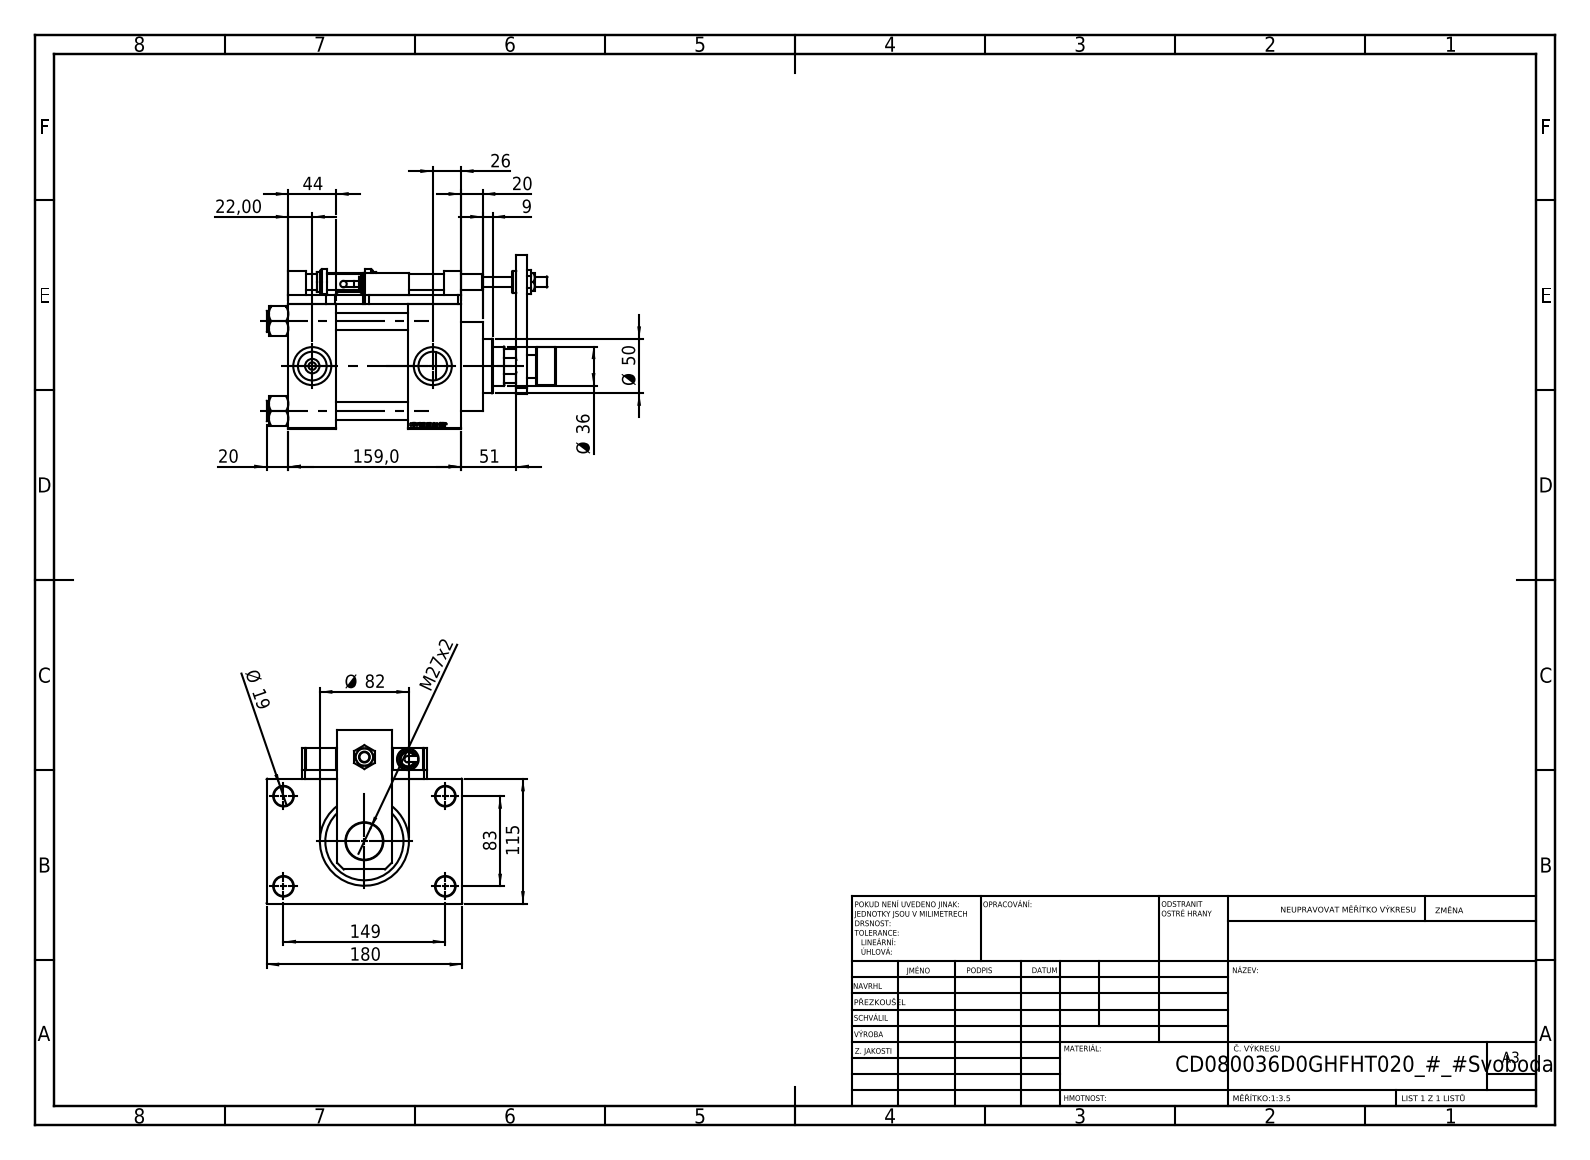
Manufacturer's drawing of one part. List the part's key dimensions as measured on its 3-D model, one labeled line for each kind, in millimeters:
Part name (STEP PRODUCT): V215CD_NUT_M5_D; V215CD_SWITCH_Q_BLOK; V215CD_SWITCH_Q_NUT10; V215CR_ROD_END_F (+7 more)
STEP written by: SolidWorks 2019 (CONFIG_CONTROL_DESIGN)
Units: millimetres
Bodies: 25 solids, 1393 faces (670 planar, 160 cylindrical, 563 other)
Overall size (bounding box): 266 × 180 × 160
Volume: 2 297 000 mm³ · Surface area: 393 388 mm²
Round holes (diameter × count): ⌀8.5 ×4, ⌀13.5 ×4, ⌀16 ×4, ⌀18 ×4, ⌀7 ×2, ⌀26.44 ×2, ⌀35 ×2, ⌀10 ×1, ⌀14 ×1, ⌀25.5 ×1, ⌀27 ×1, ⌀36 ×1
Round bosses / shafts (diameter × count): ⌀19 ×4, ⌀20 ×3, ⌀16 ×2, ⌀14 ×2, ⌀6 ×2, ⌀86 ×1, ⌀82 ×1, ⌀50 ×1
Partial cylindrical surfaces — rounded edges, fillets, slot ends (radius × count): R7.5 ×4
Main face-to-face distances: 115, 110, 8, 123, 66, 49, 44, 159, 32.5, 20
Hole centre spacings: 33.15, 58.48, 82.7, 85.28, 89.24, 115.85, 142.43, 32
